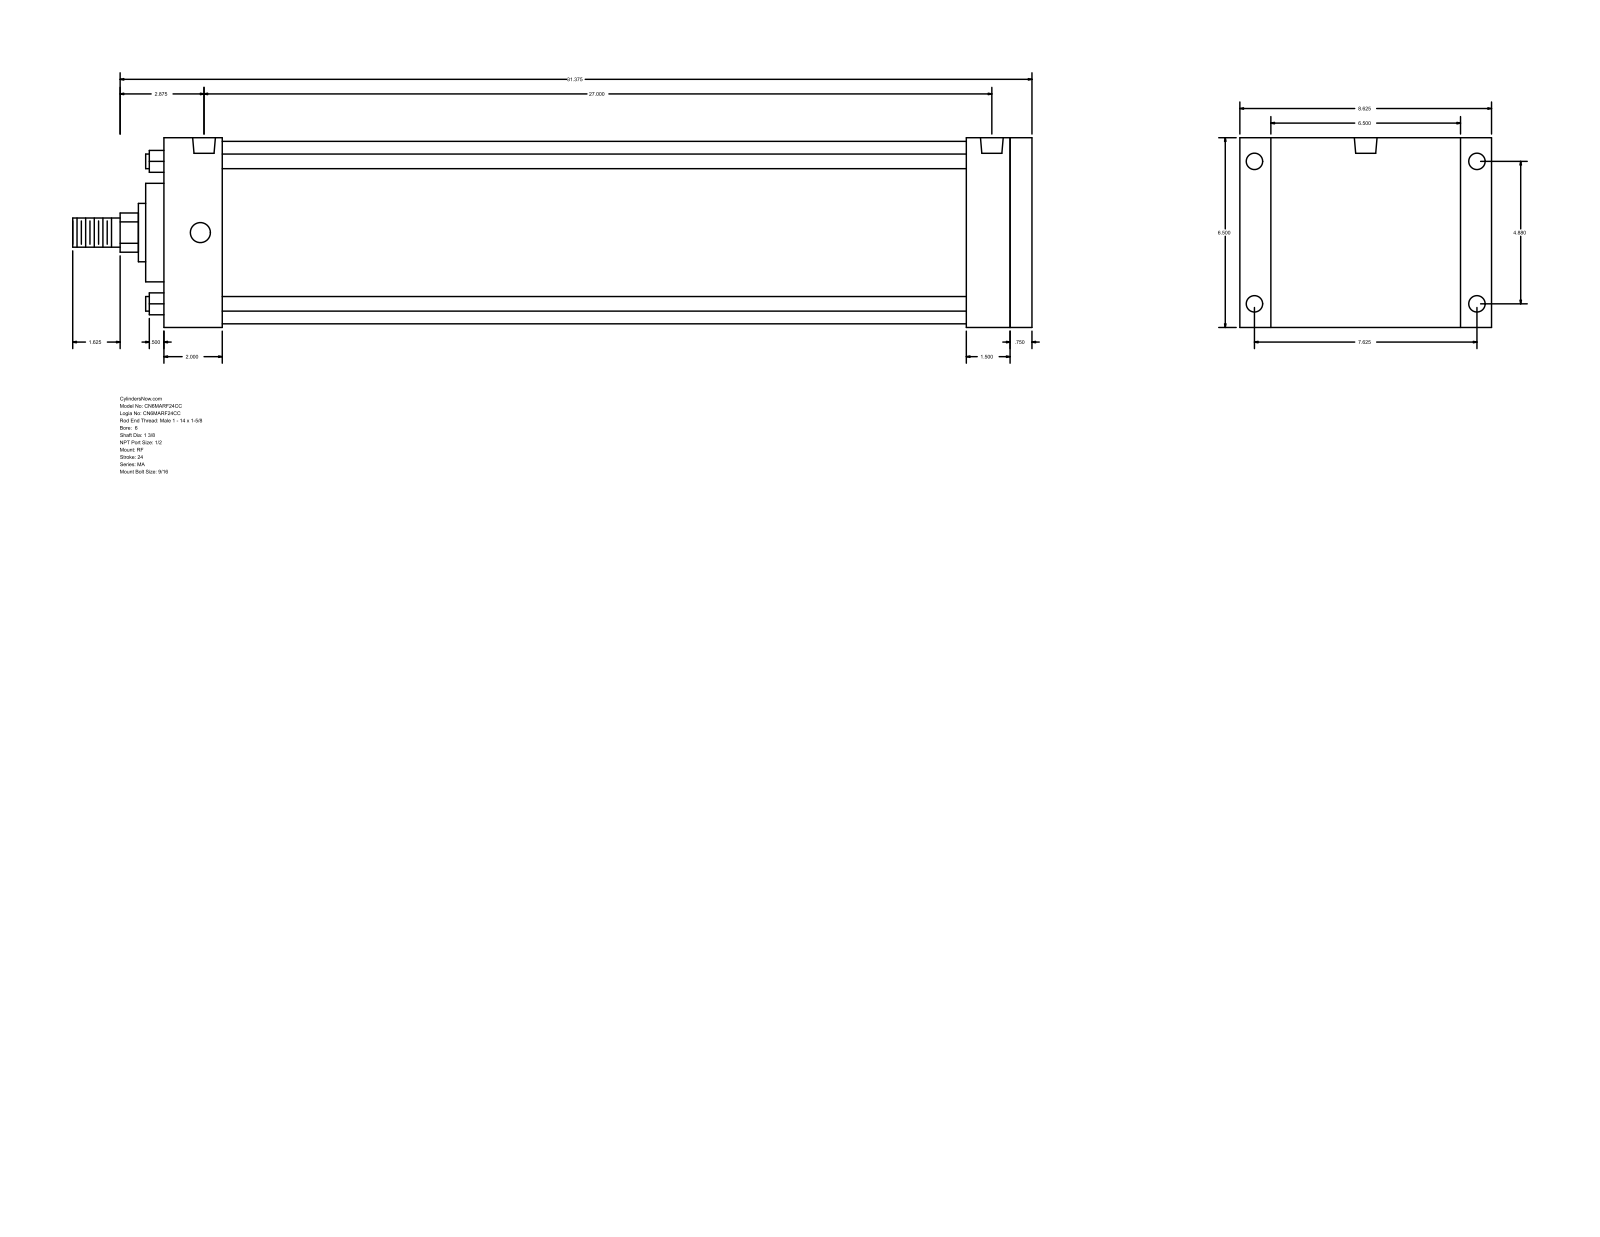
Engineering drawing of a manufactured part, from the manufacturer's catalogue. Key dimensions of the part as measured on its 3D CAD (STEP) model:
Part name (STEP PRODUCT): MA_RF__0600_1.375
STEP written by: GSSL Pune (CONFIG_CONTROL_DESIGN)
Units: millimetres
Bodies: 0 solids, 94 faces (65 planar, 29 cylindrical, 0 other)
Overall size (bounding box): 838.2 × 219.07 × 165.1
Round holes (diameter × count): ⌀14.29 ×4, ⌀17.46 ×4, ⌀19.77 ×2
Round bosses / shafts (diameter × count): ⌀12.7 ×4, ⌀158.75 ×1, ⌀85.72 ×1, ⌀50.8 ×1, ⌀34.92 ×1, ⌀25.4 ×1
Partial cylindrical surfaces — rounded edges, fillets, slot ends (radius × count): R17.06 ×1
Main face-to-face distances: 165.1, 758.82, 739.78, 19.04, 57.15, 50.8, 688.98, 708.02, 701.67, 650.87
Hole centre spacings: 123.96, 193.68, 229.95, 688.98, 3.18, 685.8
